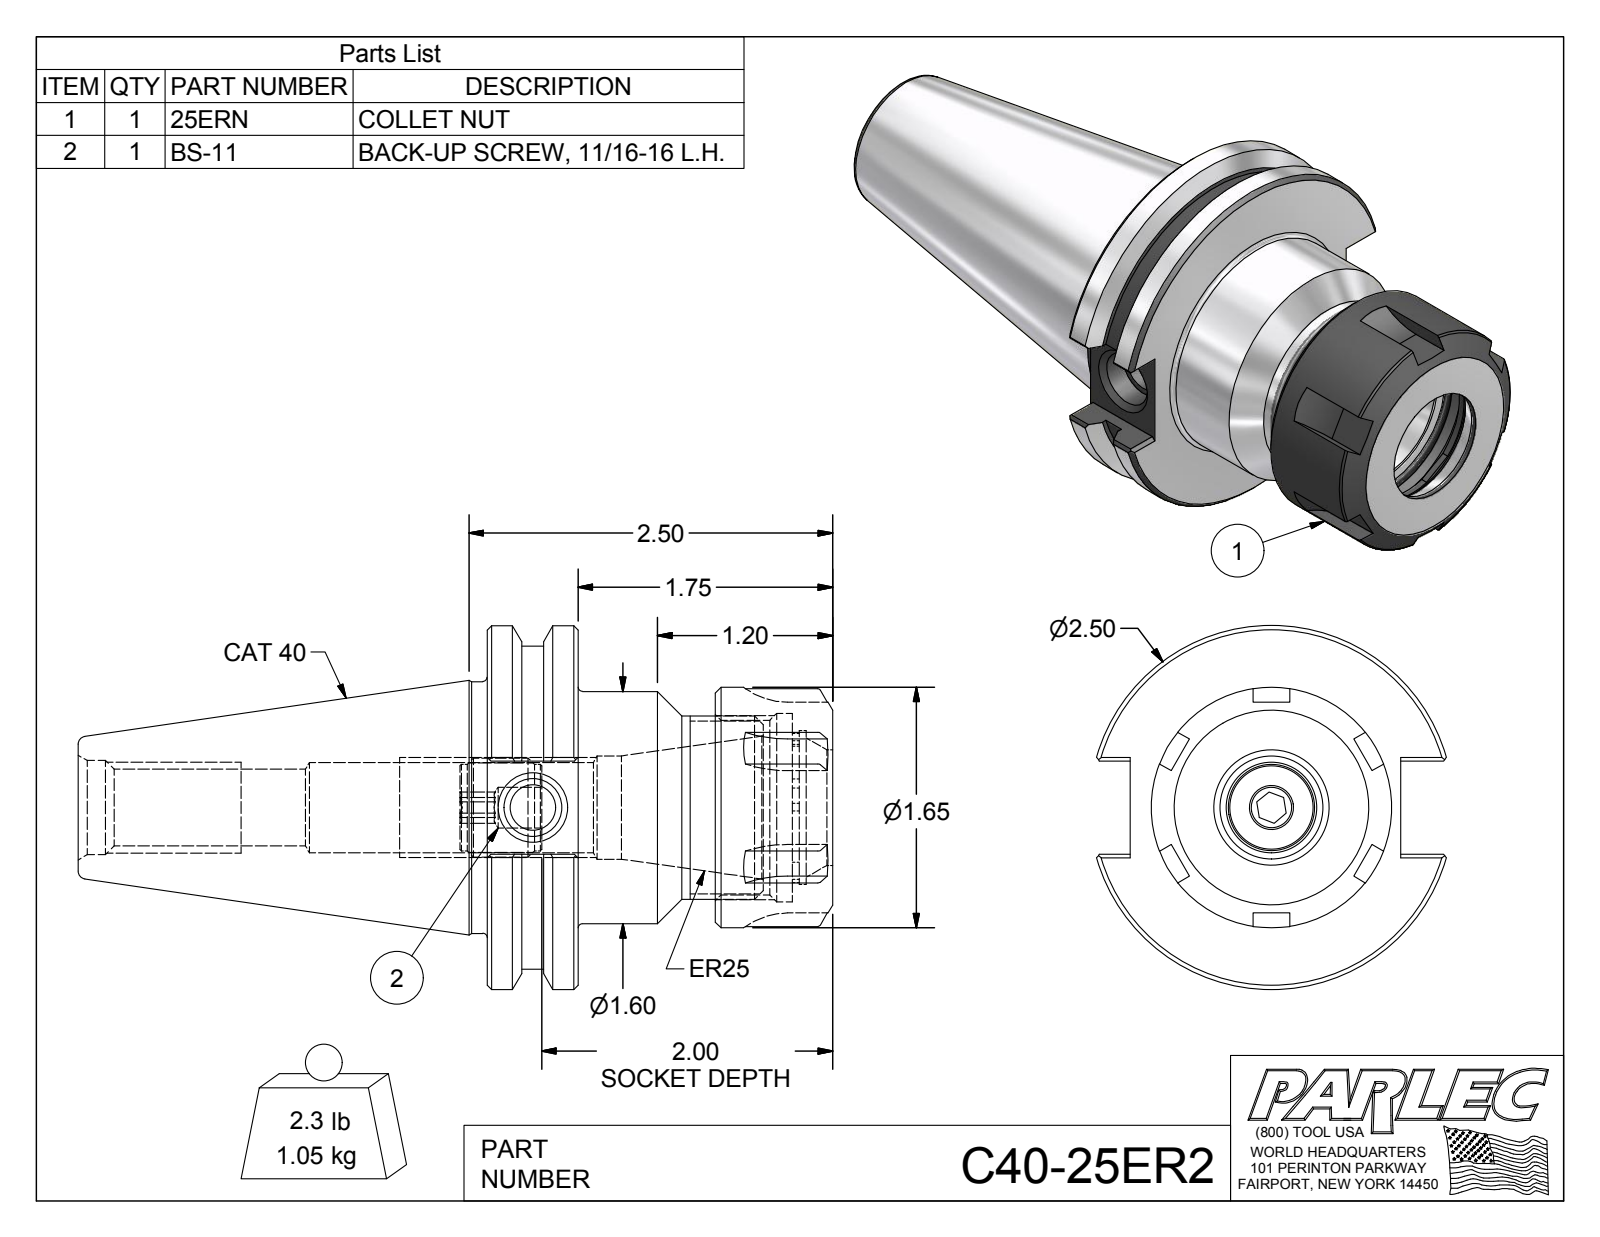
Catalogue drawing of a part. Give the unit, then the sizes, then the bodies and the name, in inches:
Units: inches
Overall size (bounding box): 5.188 × 2.5 × 2.403
Round holes (diameter × count): ⌀0.28 ×1, ⌀0.315 ×1, ⌀0.396 ×1, ⌀0.527 ×1, ⌀0.62 ×1, ⌀0.648 ×1, ⌀0.71 ×1, ⌀0.794 ×1, ⌀1.057 ×1, ⌀1.201 ×1, ⌀1.294 ×1
Round bosses / shafts (diameter × count): ⌀2.5 ×1, ⌀2.219 ×1, ⌀1.73 ×1, ⌀1.654 ×1, ⌀1.595 ×1, ⌀1.26 ×1, ⌀0.681 ×1, ⌀0.595 ×1
Partial cylindrical surfaces — rounded edges, fillets, slot ends (radius × count): R0.5 ×6, R0.472 ×1, R0.515 ×1
Main face-to-face distances: 0.625, 2.375, 1.75, 1.568, 0.943, 0.807, 2.099, 1.474, 0.531, 0.276
Volume: 8.337 in³ · Surface area: 52.26 in²
Bodies: 3 solids, 143 faces (67 planar, 35 cylindrical, 41 other)
Part name (STEP PRODUCT): C40-25ER2; C40-25ER2-1; 25ERN; BS-11
STEP written by: Autodesk Inventor 2012 (AUTOMOTIVE_DESIGN)
